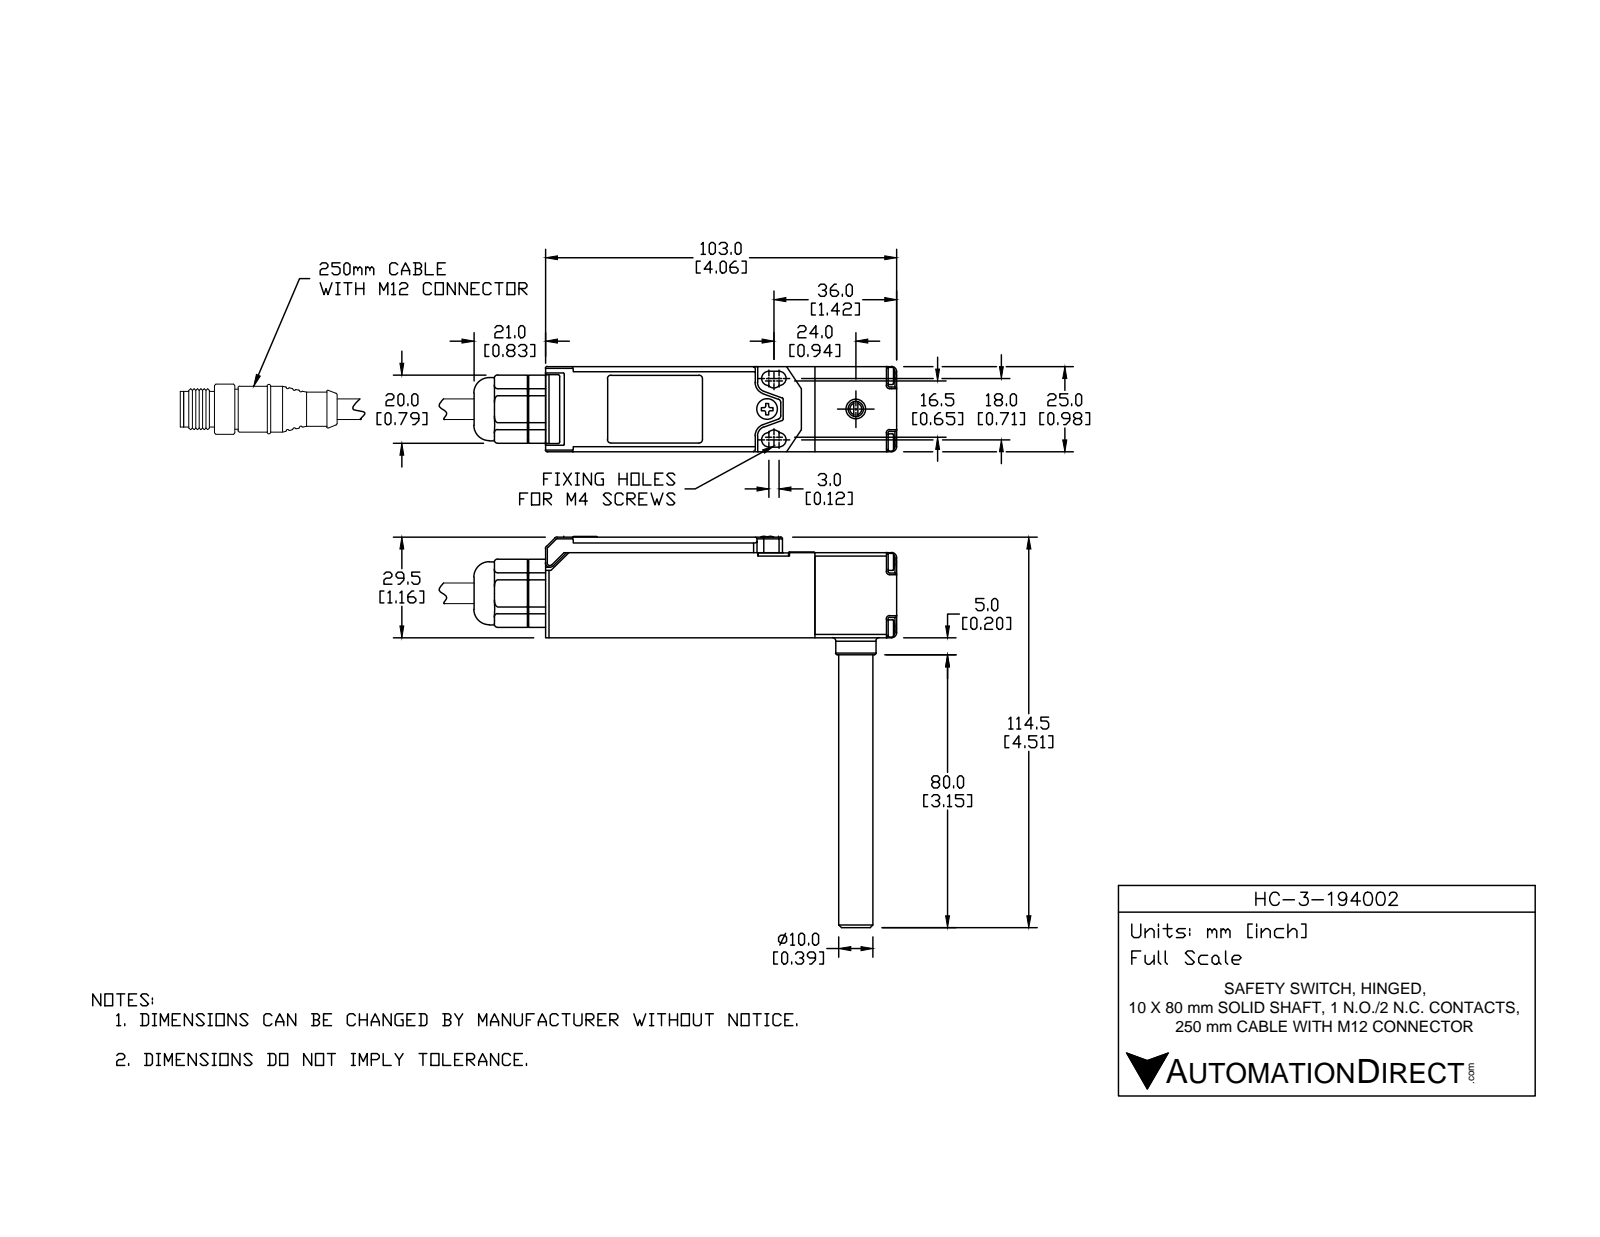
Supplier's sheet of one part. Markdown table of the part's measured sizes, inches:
| quantity | value |
| --- | --- |
| part name | HC-3-194002 |
| STEP written by | SolidWorks 2014 (AUTOMOTIVE_DESIGN) |
| units | inches |
| bodies | 13 solids, 1848 faces (866 planar, 583 cylindrical, 399 other) |
| overall size | 4.517 × 4.055 × 0.984 |
| volume | 2.231 in³ |
| surface area | 52.85 in² |
| round holes (diameter × count) | 0.126 × 5, 0.094 × 4, 0.059 × 2, 0.063 × 2, 0.071 × 2, 0.087 × 2, 0.142 × 2, 0.63 × 2, 0.055 × 1, 0.081 × 1, 0.098 × 1, 0.102 × 1 |
| round bosses / shafts (diameter × count) | 0.102 × 5, 0.197 × 4, 0.079 × 4, 0.138 × 2, 0.394 × 1, 0.386 × 1, 0.256 × 1, 0.228 × 1 |
| partial cylindrical surfaces (radius × count) | 0.02 × 225, 0.004 × 24, 0.039 × 21, 0.012 × 12, 0.059 × 6, 0.083 × 6, 0.11 × 6, 0.138 × 6 |
| main face-to-face distances | 0.984, 0.079, 0.071, 0.913, 0.177, 0.906, 0.098, 0.039, 0.827, 0.087 |
| hole center spacings | 0.543, 0.768, 0.171, 0.187, 0.245, 0.414, 0.423, 0.426 |
